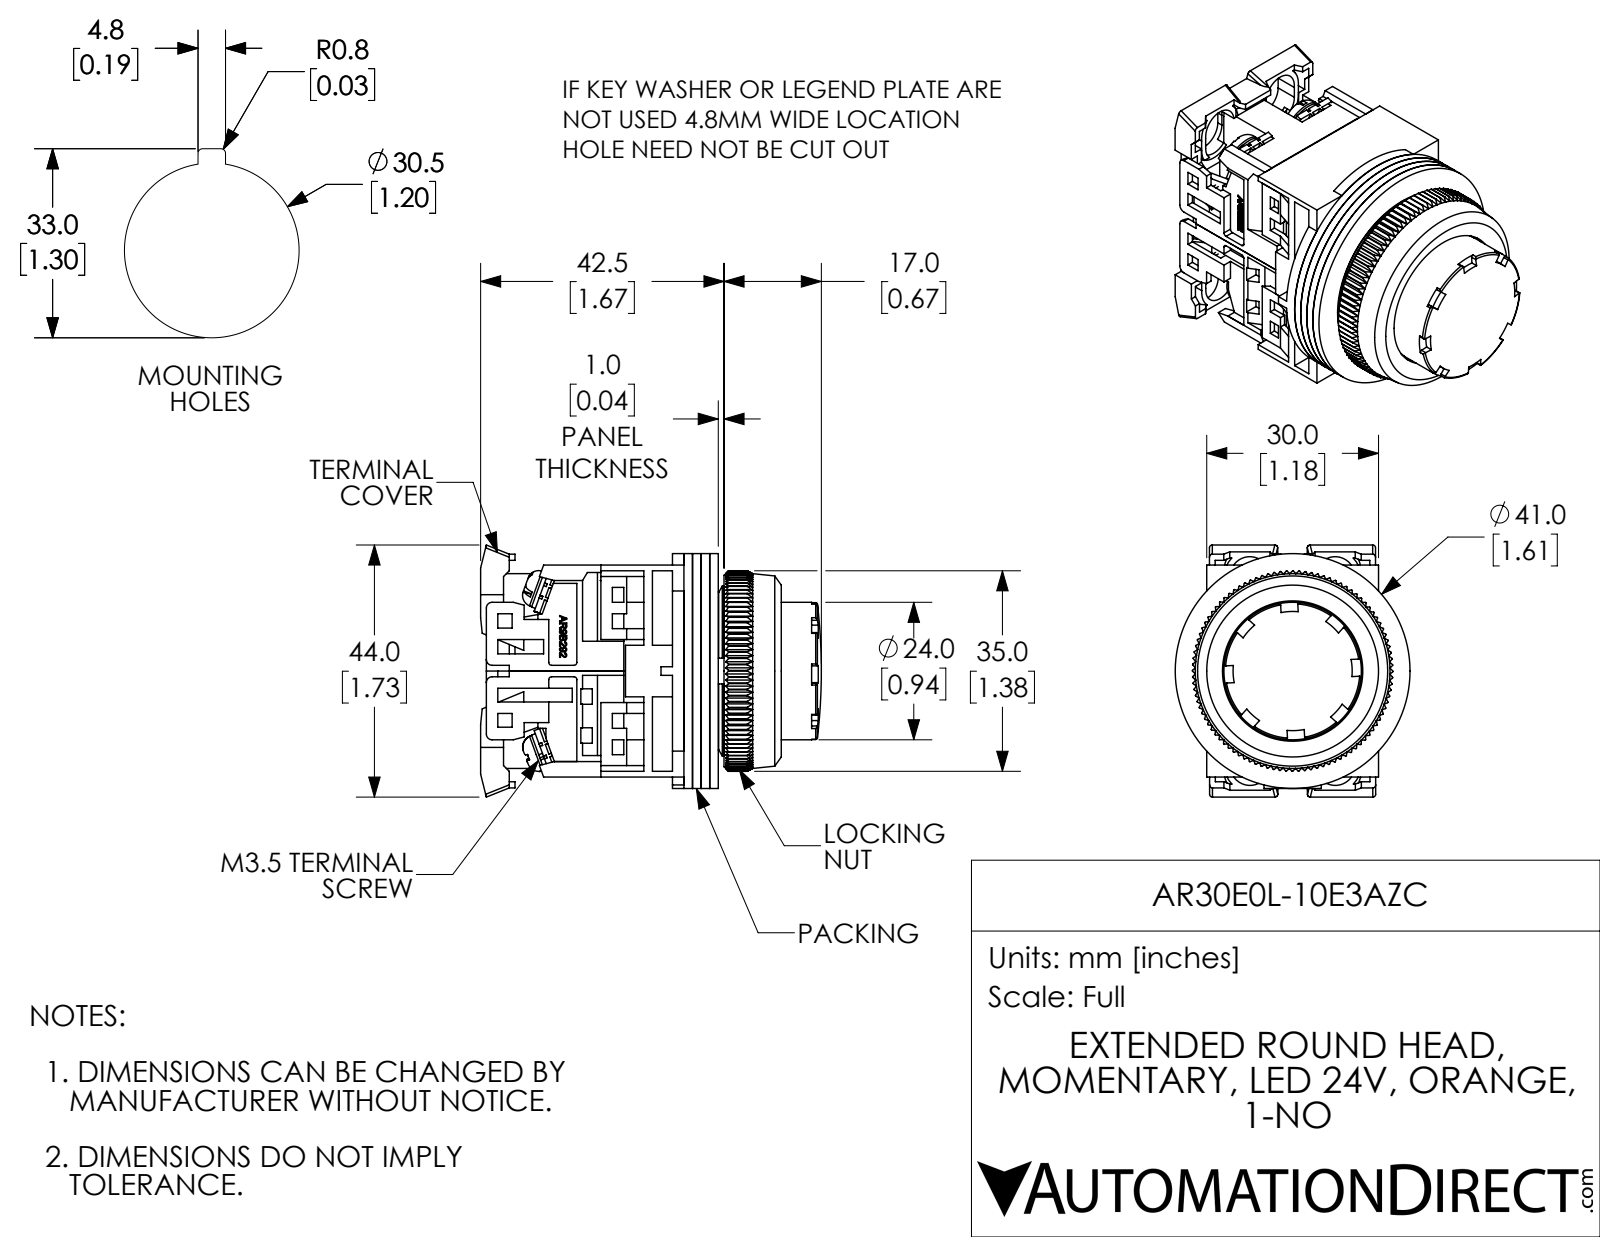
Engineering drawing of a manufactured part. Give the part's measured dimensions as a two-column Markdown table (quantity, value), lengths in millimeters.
| quantity | value |
| --- | --- |
| part name | AR30E0L-10E3AZC |
| STEP written by | SolidWorks 2017 (AUTOMOTIVE_DESIGN) |
| units | millimeters |
| bodies | 25 solids, 2022 faces (1378 planar, 323 cylindrical, 321 other) |
| overall size | 59.5 × 44 × 41 |
| volume | 34 720 mm³ |
| surface area | 38 610 mm² |
| round holes (diameter × count) | 3.5 × 8, 3.6 × 4, 3 × 1, 12 × 1, 18 × 1, 18.5 × 1, 20 × 1, 24 × 1, 24.5 × 1, 28.5 × 1, 31.8 × 1 |
| round bosses / shafts (diameter × count) | 6.6 × 4, 3.5 × 4, 41 × 1, 30 × 1, 22 × 1, 19.7 × 1, 14 × 1 |
| partial cylindrical surfaces (radius × count) | 0.3 × 16, 1.5 × 16, 0.5 × 12, 1 × 4, 3.5 × 4, 4.5 × 4, 3 × 2, 10.1 × 1 |
| main face-to-face distances | 1.5, 3, 1, 4.5, 20.6, 36, 16.1, 2, 34.5, 17.5 |
| hole center spacings | 14.7, 15.5 |
